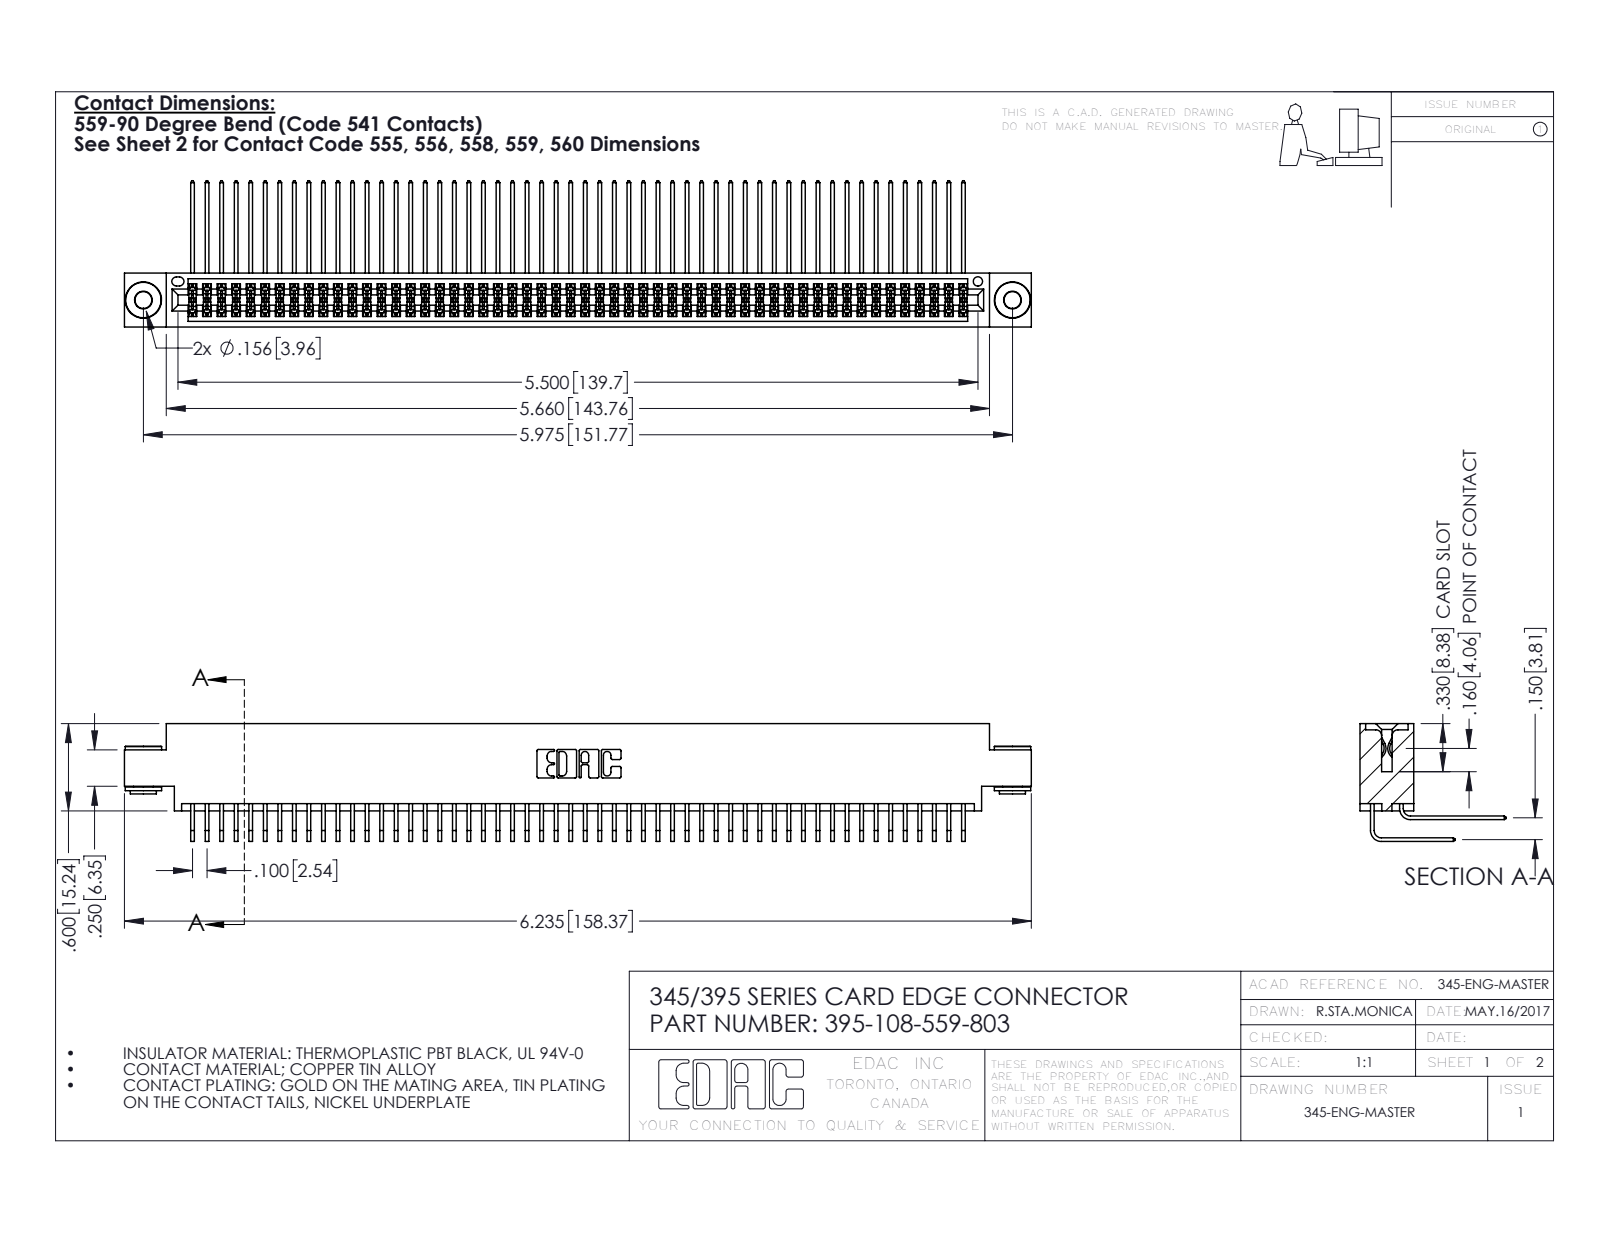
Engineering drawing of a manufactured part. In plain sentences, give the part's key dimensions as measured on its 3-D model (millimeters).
The part is named "345-292-001_559 Tail - 2; 345-250-002_345-250-002-102; 345 Part_0.170 Offset - 0.156 Dia-TH; 395-108-559-803 (+1 more)". Its 3-D file was written by "SolidWorks 2016 (CONFIG_CONTROL_DESIGN)". It is 111 solids with 5784 faces: 3874 planar, 1902 cylindrical and 8 other. Overall it measures 158.4 by 25.5 by 20.5 millimeters. Its volume is 16 000 cubic millimeters and its surface area 27 200 square millimeters. Round holes: 2 of diameter 2.9, 2 of diameter 4, 1 of diameter 1.6. Round bosses or shafts: 2 of diameter 6.4, 2 of diameter 4.6, 2 of diameter 3.5. Partial cylindrical surfaces (rounded edges, fillets, slot ends): 163 of radius 0.2, 22 of radius 0.3, 6 of radius 0.2, 6 of radius 0.8, 3 of radius 0.7, 2 of radius 0.4, 2 of radius 0.5, 2 of radius 0.6. The main face-to-face distances are 1.8, 7.6, 9.4, 5.1, 2.5, 6.9, 0.6, 5.7, 4.4, 3.8. The hole center spacings are 6.9, 145.8, 151.8.
